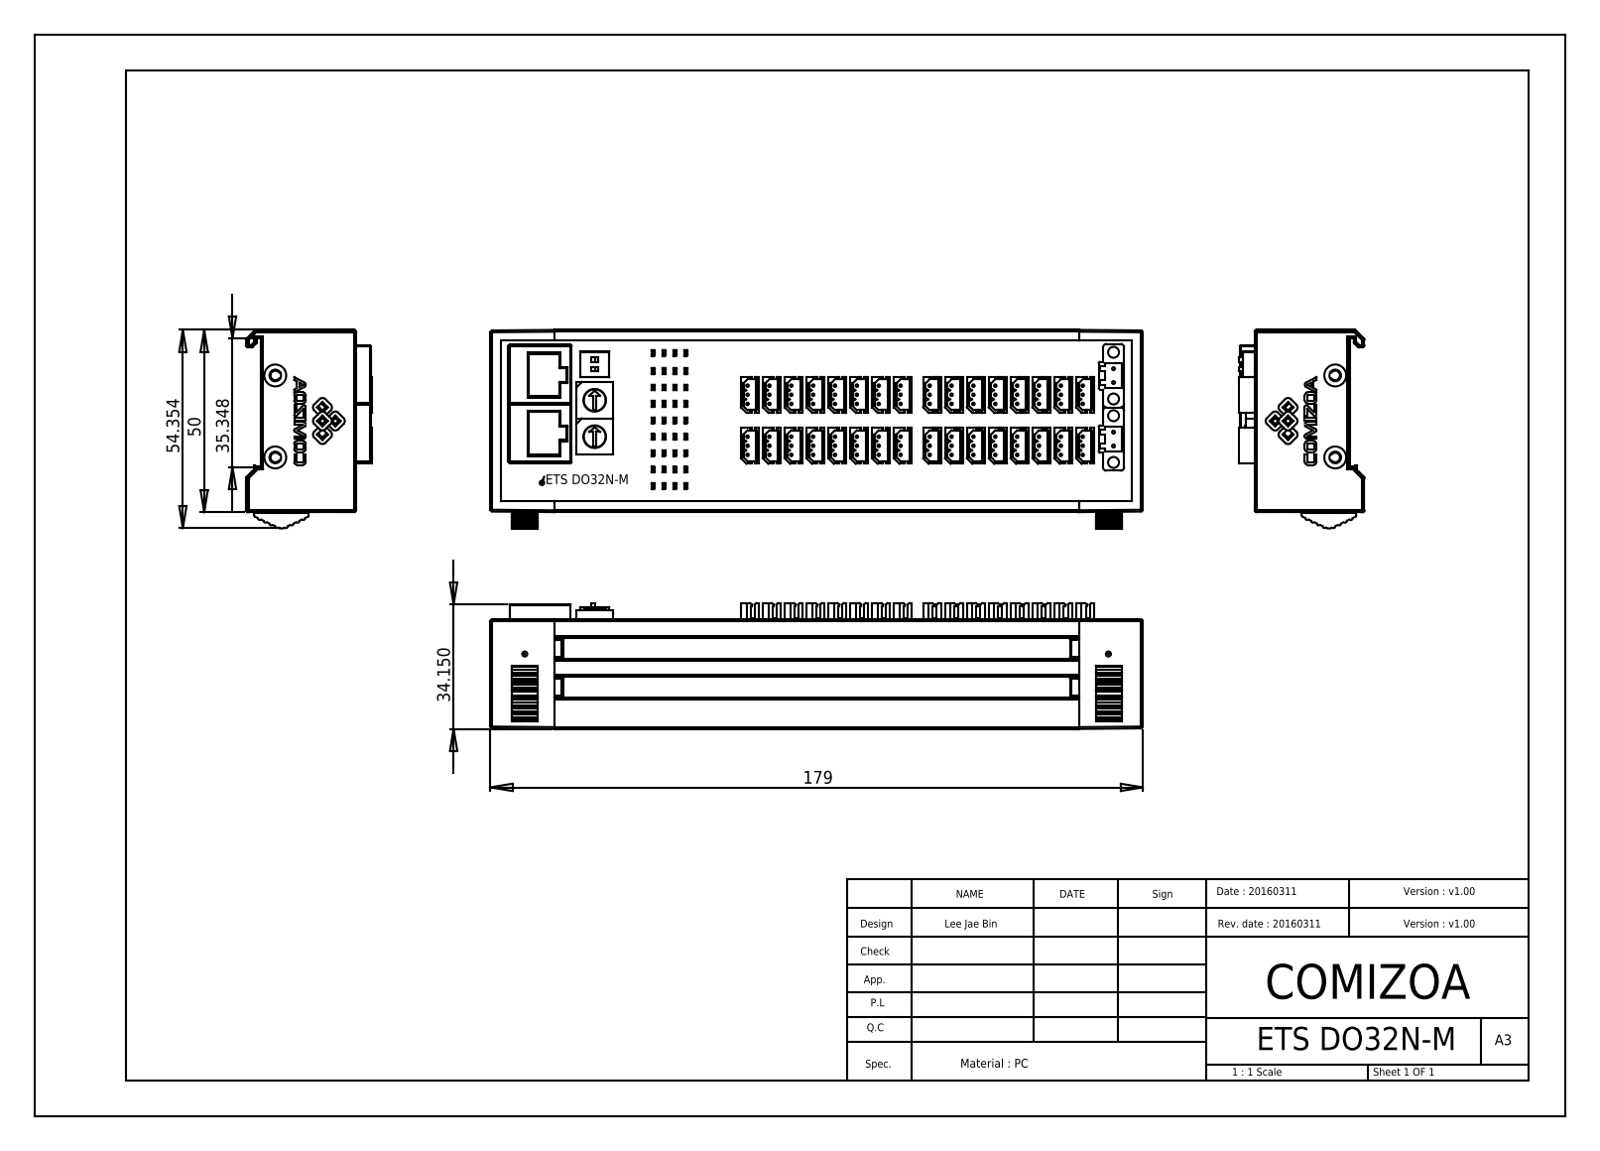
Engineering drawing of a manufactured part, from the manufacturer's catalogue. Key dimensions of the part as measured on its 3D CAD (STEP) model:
Part name (STEP PRODUCT): ETS_DO32M_ASM; ETS_32_series_bd_asm; 5267-03; LED_G (+8 more)
STEP written by: SolidWorks 2012 (CONFIG_CONTROL_DESIGN)
Units: millimetres
Bodies: 88 solids, 5268 faces (3052 planar, 1588 cylindrical, 628 other)
Overall size (bounding box): 179 × 54.49 × 34.5
Volume: 87 785 mm³ · Surface area: 114 766 mm²
Round holes (diameter × count): ⌀0.4 ×68, ⌀1 ×8, ⌀3 ×4, ⌀3.2 ×2, ⌀6.2 ×2
Round bosses / shafts (diameter × count): ⌀0.7 ×96, ⌀0.5 ×36, ⌀6 ×4, ⌀0.8 ×4, ⌀1 ×2, ⌀2 ×1
Partial cylindrical surfaces — rounded edges, fillets, slot ends (radius × count): R0.1 ×208, R0.5 ×110, R0.2 ×58, R0.3 ×42, R1.12 ×13, R0.28 ×8, R0.96 ×8, R1 ×8
Main face-to-face distances: 11.45, 2, 1.5, 13.45, 9.45, 24.6, 1.4, 23.1, 22.6, 11.15
Hole centre spacings: 6, 12, 18, 15.23, 18.44, 24, 14, 22.8
